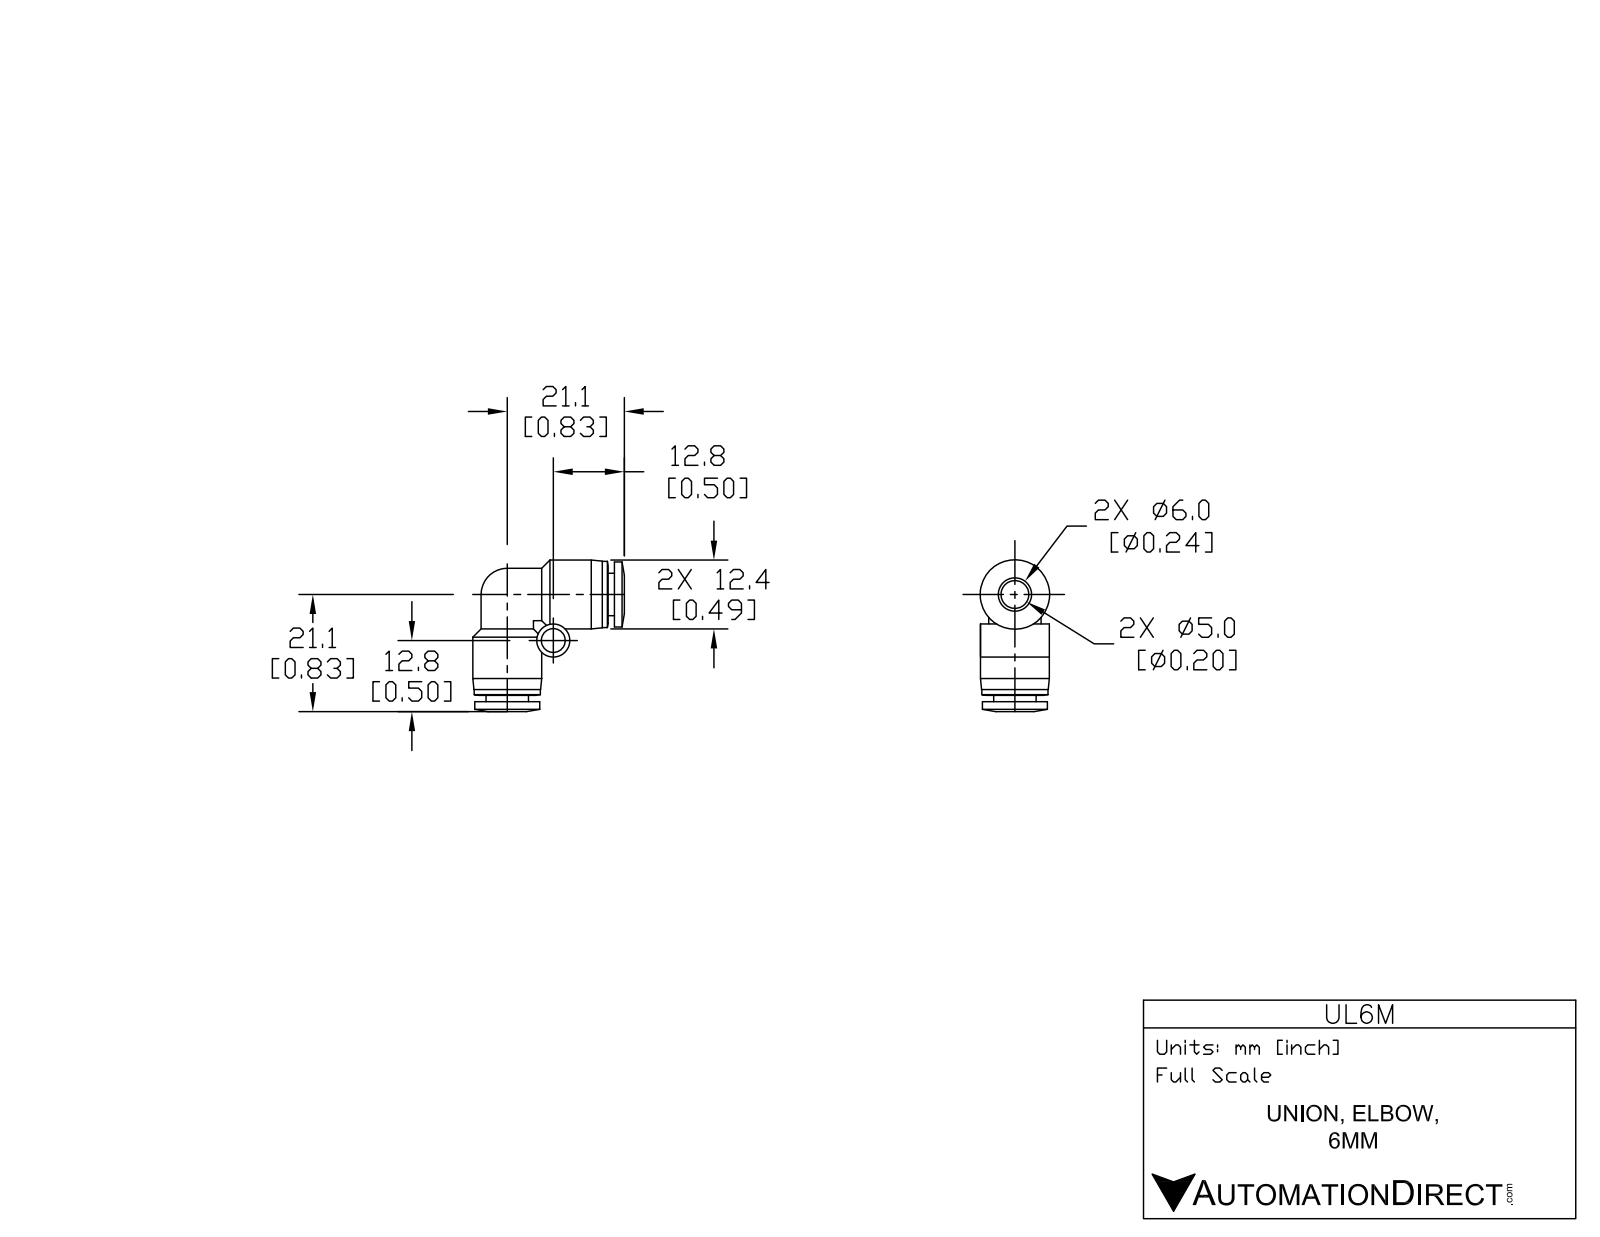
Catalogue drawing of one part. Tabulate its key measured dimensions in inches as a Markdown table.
| quantity | value |
| --- | --- |
| part name | UL6M |
| STEP written by | SolidWorks 2015 (AUTOMOTIVE_DESIGN) |
| units | inches |
| bodies | 1 solid, 68 faces (12 planar, 32 cylindrical, 24 other) |
| overall size | 1.083 × 1.083 × 0.492 |
| volume | 0.19 in³ |
| surface area | 4.745 in² |
| round holes (diameter × count) | 0.197 × 2, 0.248 × 2, 0.165 × 1 |
| round bosses / shafts (diameter × count) | 0.492 × 2, 0.472 × 2, 0.465 × 2, 0.374 × 2, 0.303 × 2, 0.236 × 1 |
| main face-to-face distances | 0.045, 0.53, 0.575, 0.492, 0.646, 0.116, 0.071, 0.488, 0.041, 0.087 |
